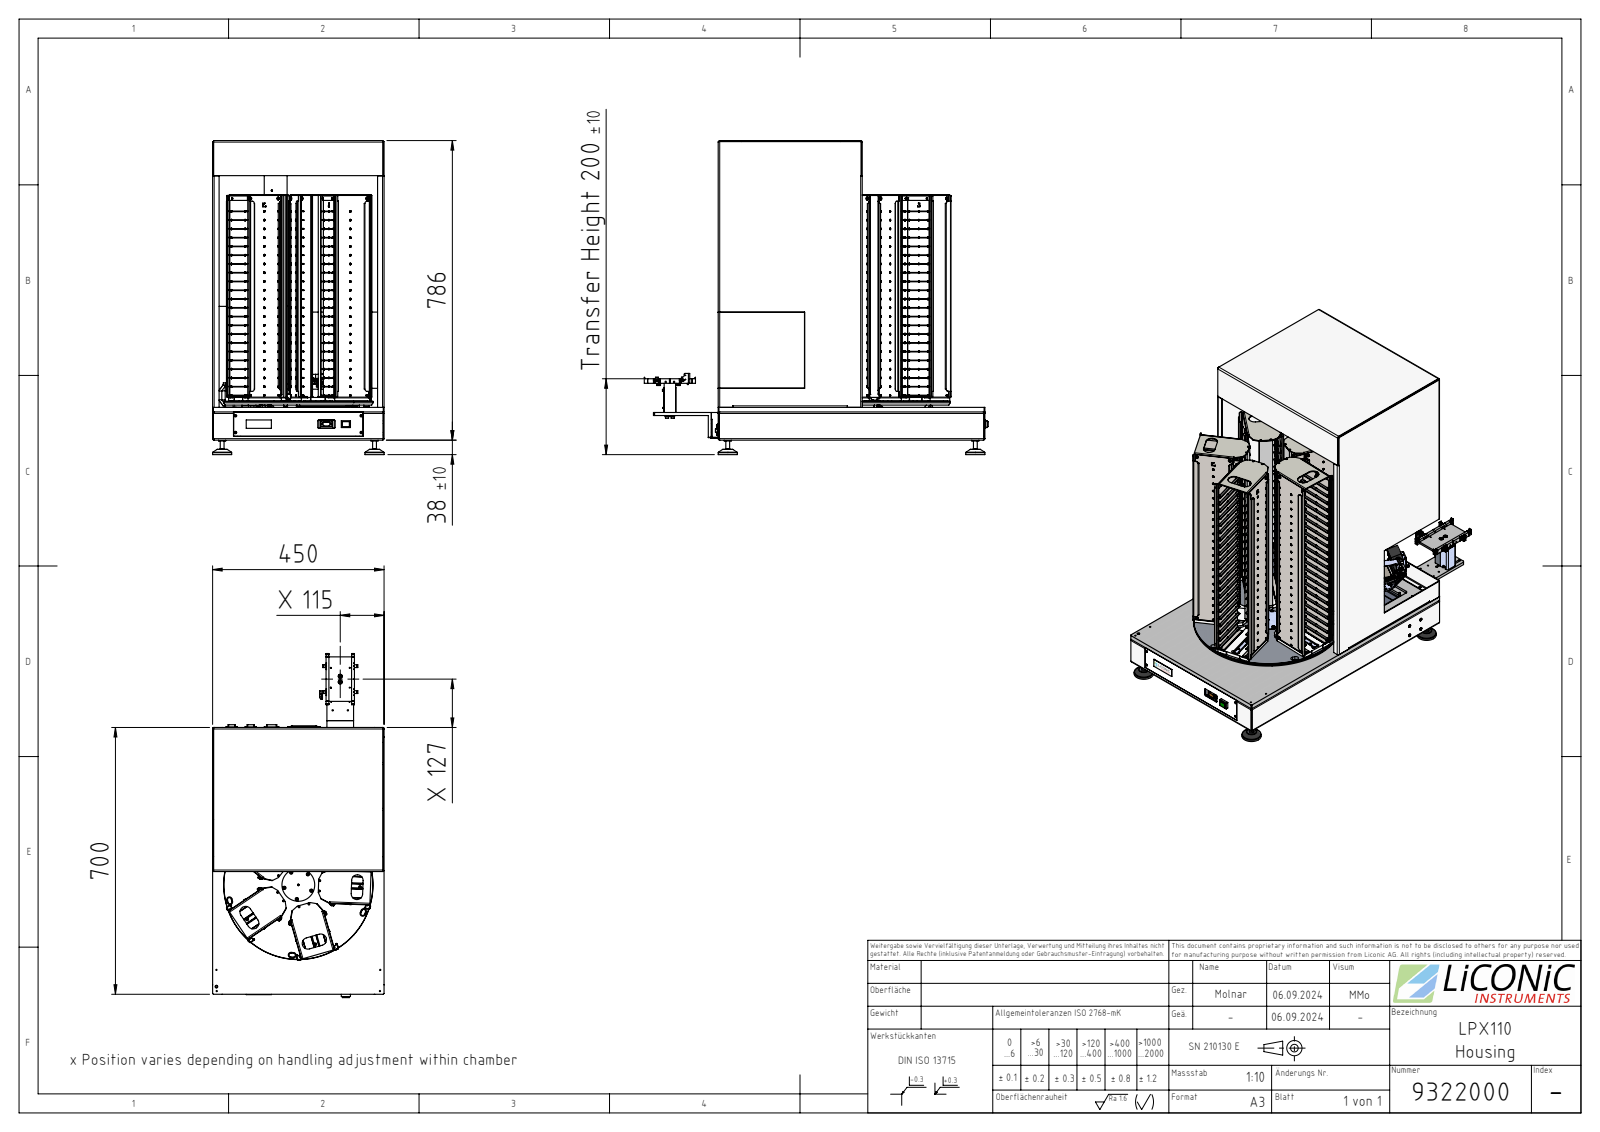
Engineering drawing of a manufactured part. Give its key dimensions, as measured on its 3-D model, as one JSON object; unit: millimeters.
{"part_name": "9322000", "step_written_by": "SolidWorks 2022 (AUTOMOTIVE_DESIGN)", "units": "millimeters", "bodies": {"solids": 36, "faces": 5696, "planar": 3214, "cylindrical": 2377, "other": 105}, "overall_size": [902.84, 824, 450.01], "volume_mm3": 8846000, "surface_area_mm2": 4642000, "round_holes": [[4, 50], [2.5, 49], [3.3, 25], [4.2, 23], [6.5, 17], [3, 12], [6, 10], [3.1, 8], [7.1, 8], [12, 7], [3.4, 6], [5.3, 6]], "round_bosses_or_shafts": [[50.01, 4], [10, 4], [1.5, 3], [392, 1], [86, 1], [15.5, 1], [14.5, 1]], "partial_cylinders_radius": [[0.1, 572], [0.25, 572], [2, 270], [2.5, 110], [5, 65], [1, 56], [4, 25], [3, 18]], "face_to_face_distances": [2, 448, 72, 784, 12, 86, 74, 84, 450, 446], "hole_center_spacings": [23, 46, 69, 92, 115, 138, 161, 184]}
